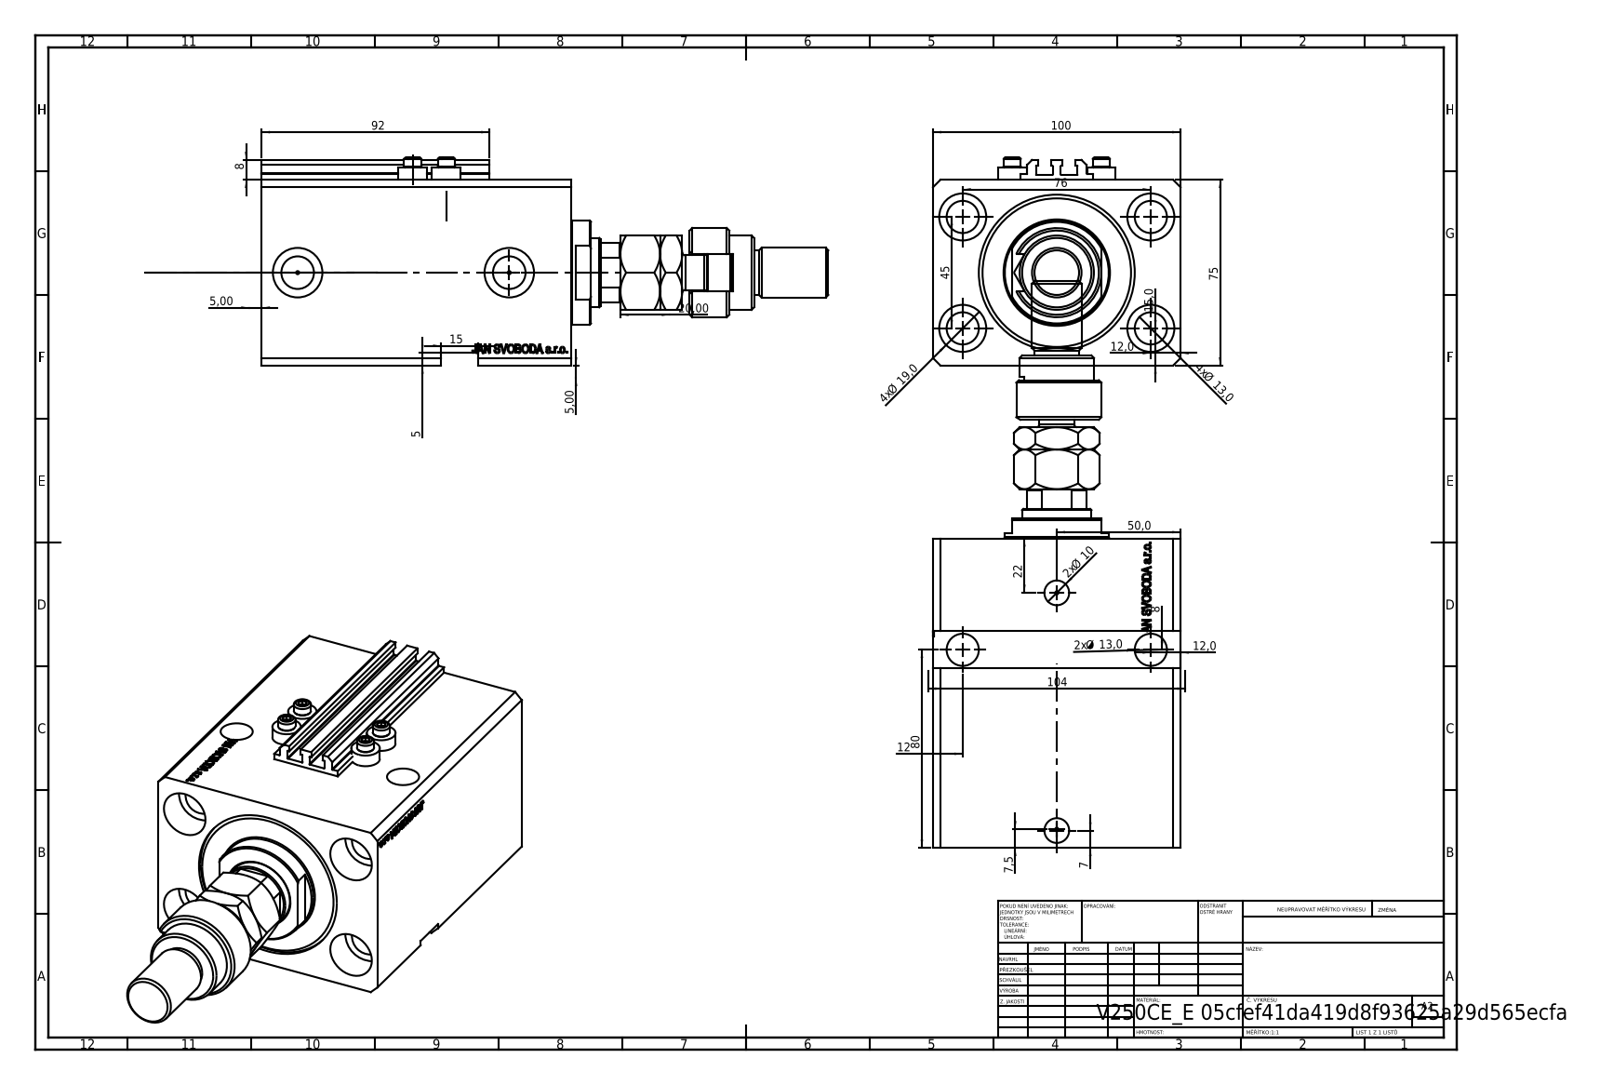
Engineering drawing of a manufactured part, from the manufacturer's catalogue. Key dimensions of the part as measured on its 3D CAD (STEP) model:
Part name (STEP PRODUCT): FEMALE_PART_FOR_DFA; V250CE_E; V250CE_VC_E; MFA (+2 more)
STEP written by: SolidWorks 2019 (CONFIG_CONTROL_DESIGN)
Units: millimetres
Bodies: 10 solids, 1173 faces (563 planar, 139 cylindrical, 471 other)
Overall size (bounding box): 228.9 × 100 × 84
Volume: 831 736 mm³ · Surface area: 162 342 mm²
Round holes (diameter × count): ⌀13 ×6, ⌀1.25 ×4, ⌀4 ×4, ⌀19 ×4, ⌀10 ×2, ⌀13.16 ×2, ⌀20 ×2, ⌀18.5 ×1, ⌀28 ×1, ⌀50 ×1, ⌀63 ×1
Round bosses / shafts (diameter × count): ⌀11.6 ×4, ⌀7 ×4, ⌀42 ×1, ⌀36 ×1, ⌀30 ×1, ⌀22 ×1, ⌀20 ×1, ⌀18 ×1
Partial cylindrical surfaces — rounded edges, fillets, slot ends (radius × count): R0.2 ×10, R7.5 ×1, R12 ×1, R13.5 ×1
Main face-to-face distances: 75, 100, 125, 11.9, 113.1, 98.4, 86.5, 26.6, 30, 48.4
Hole centre spacings: 44.16, 76, 13.6, 20.72, 27.59, 33.62, 36, 38.48
